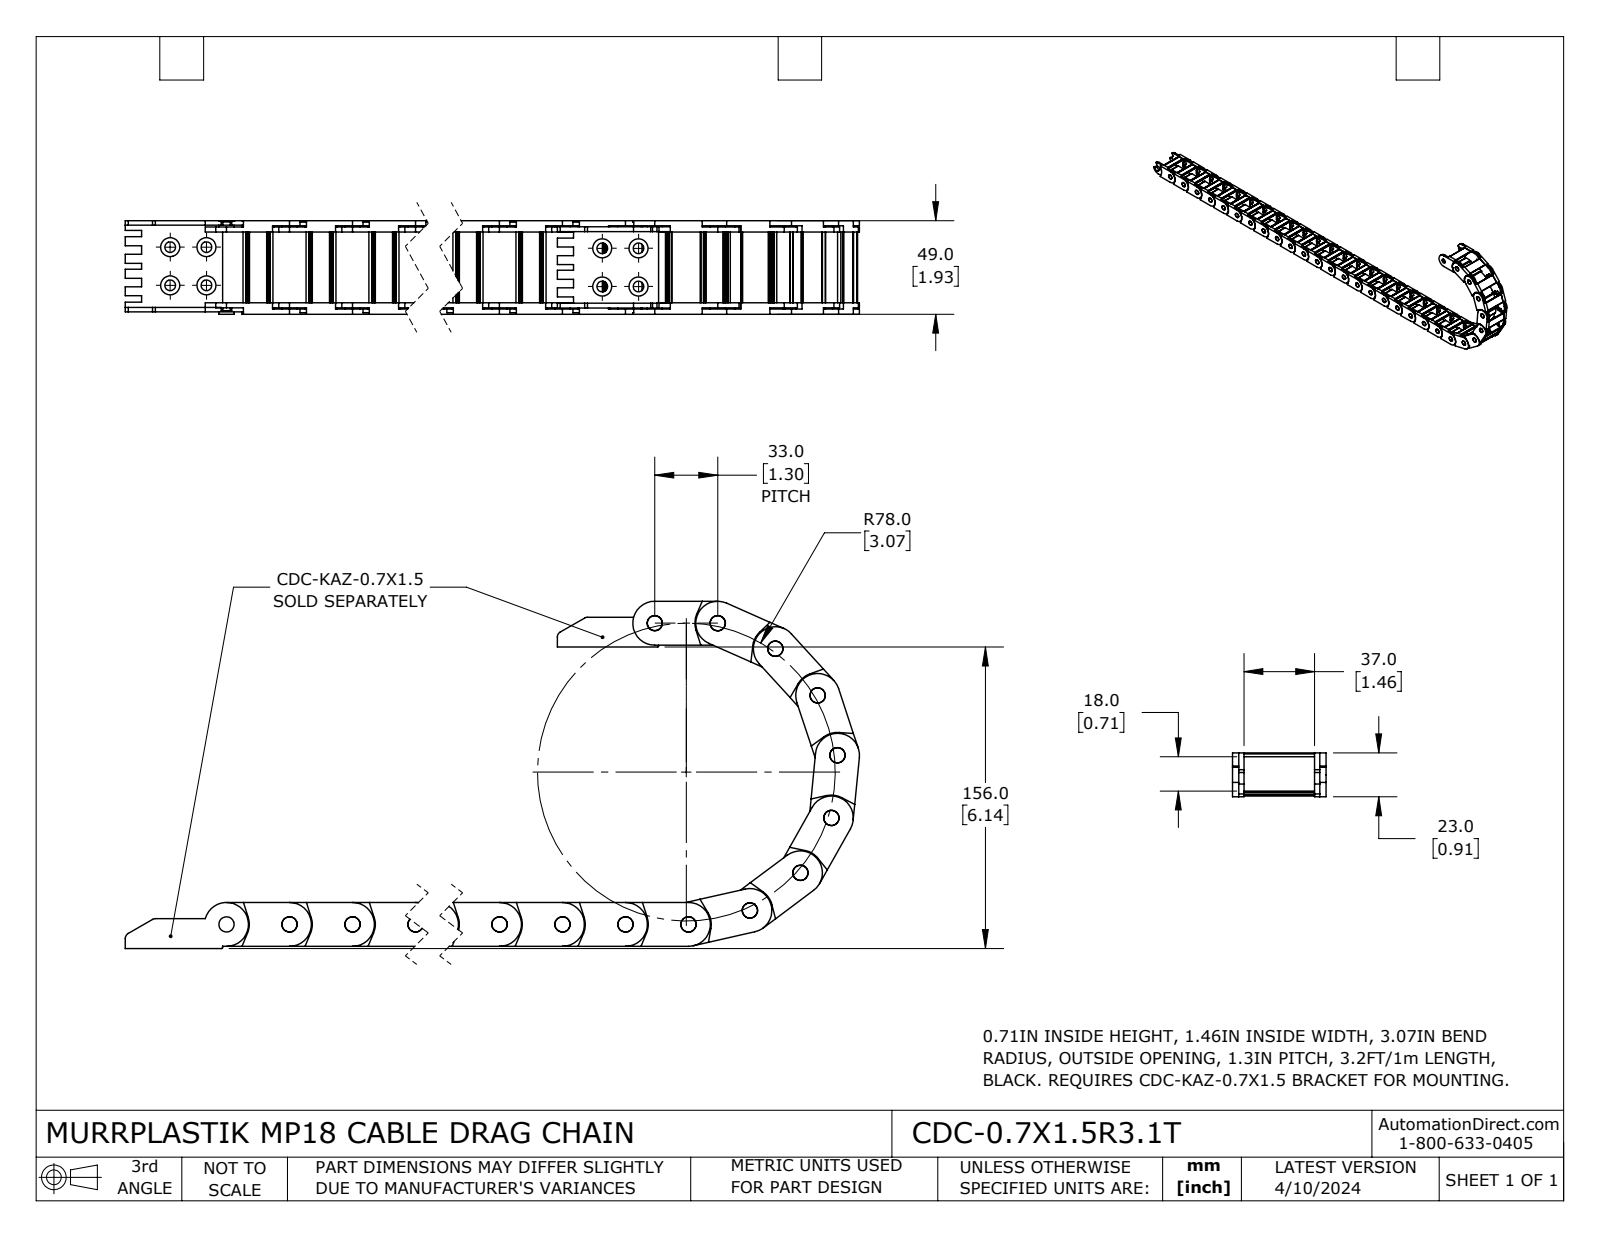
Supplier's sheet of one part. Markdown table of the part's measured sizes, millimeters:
| quantity | value |
| --- | --- |
| part name | CDC-0.7X1.5R3.1T |
| STEP written by | SolidWorks 2023 (CONFIG_CONTROL_DESIGN) |
| units | millimeters |
| bodies | 30 solids, 2280 faces (1110 planar, 1170 cylindrical, 0 other) |
| overall size | 826.74 × 180.72 × 49 |
| volume | 289 410 mm³ |
| surface area | 238 745 mm² |
| round holes (diameter × count) | 8 × 30 |
| round bosses / shafts (diameter × count) | 8 × 1 |
| partial cylindrical surfaces (radius × count) | 0.5 × 120, 1.5 × 120, 0.2 × 60, 0.3 × 60, 11.5 × 31, 11.95 × 31, 5 × 30, 5.45 × 30 |
| main face-to-face distances | 43, 2.7, 3.3, 6, 49, 45.7, 39.7, 46.3, 0.6, 40.3 |
| hole center spacings | 33, 66, 99, 132, 165, 198, 231, 264 |
